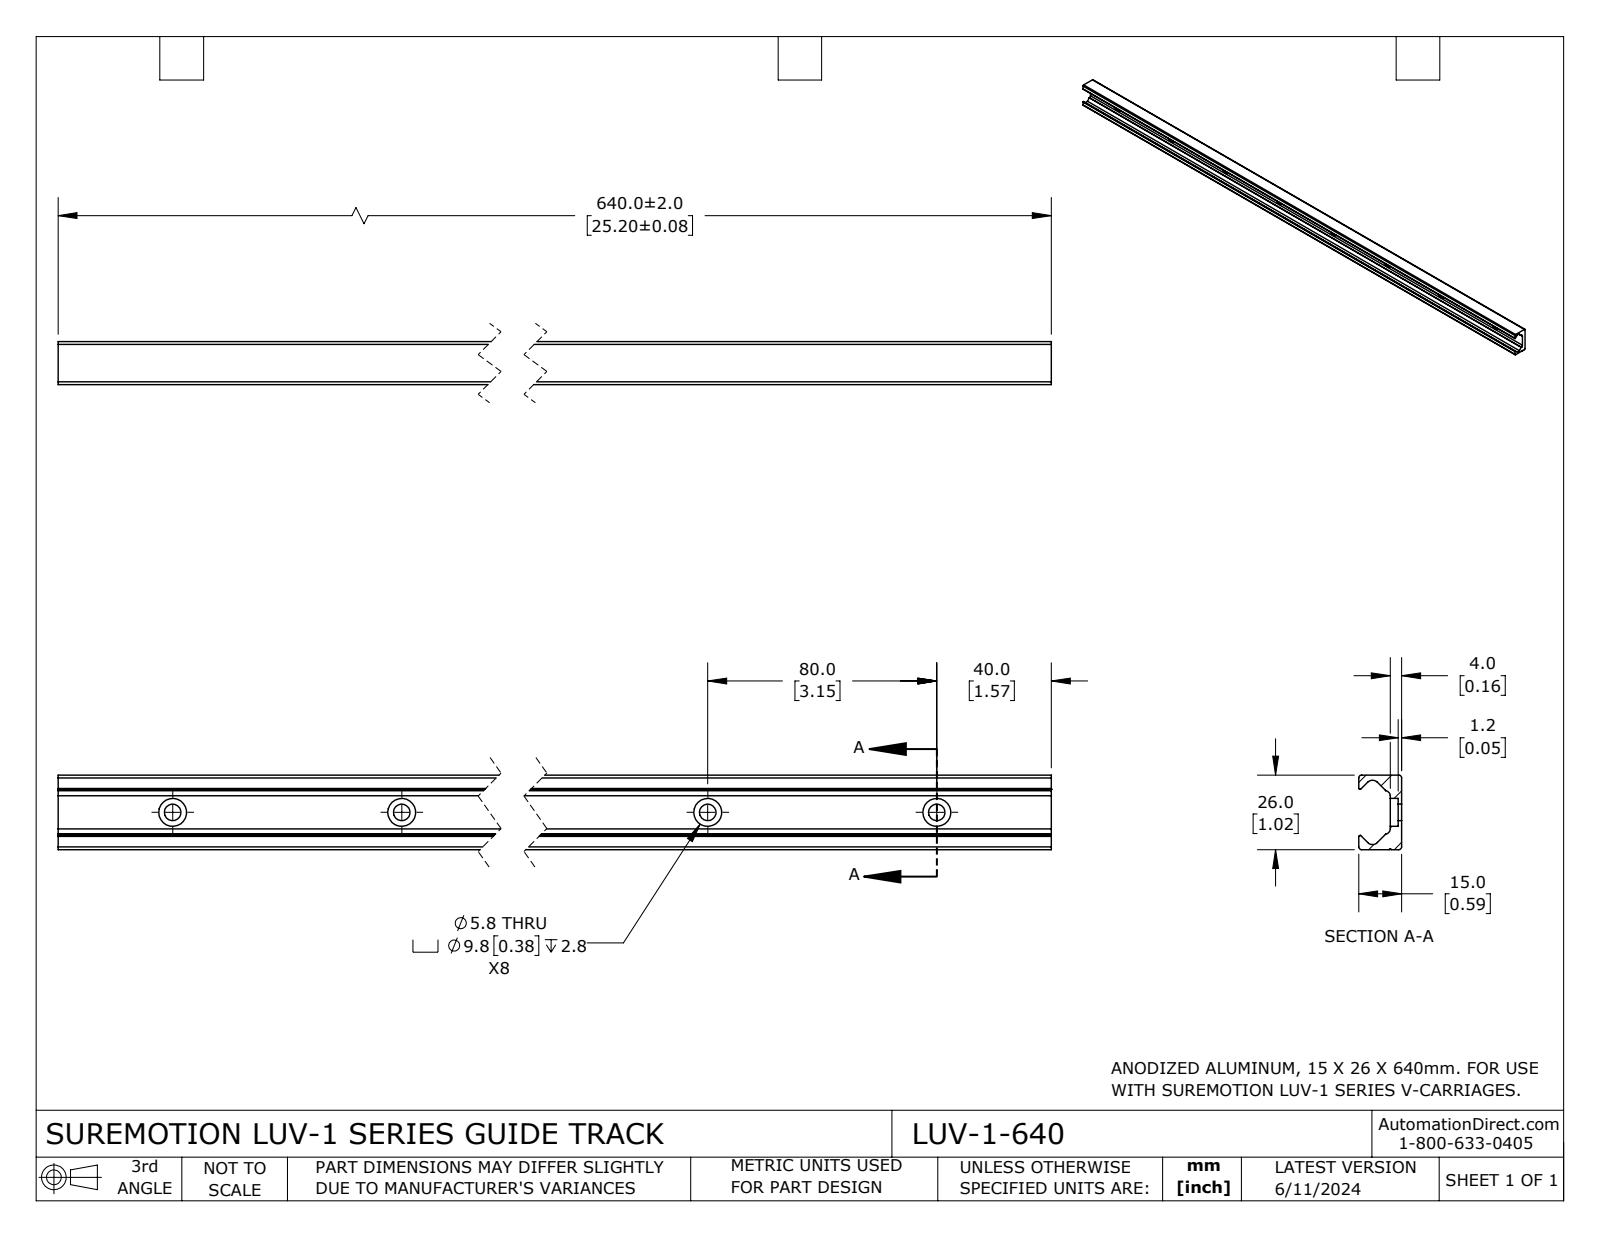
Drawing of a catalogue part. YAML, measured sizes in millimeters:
part_name: "LUV-1-640"
step_written_by: "SolidWorks 2023 (CONFIG_CONTROL_DESIGN)"
units: millimeters
bodies: {solids: 1, faces: 68, planar: 21, cylindrical: 47, other: 0}
overall_size: [640, 26.01, 15.01]
volume: 115238
surface_area: 68068
round_holes:
  - {diameter: 5.79, count: 8}
  - {diameter: 9.75, count: 8}
partial_cylinders:
  - {radius: 0.99, count: 4}
  - {radius: 0.51, count: 2}
  - {radius: 0.64, count: 2}
  - {radius: 0.76, count: 2}
  - {radius: 1.78, count: 2}
  - {radius: 2.39, count: 2}
  - {radius: 0.33, count: 1}
face_to_face_distances: [26.02, 4.01, 15.02, 11.01, 17.27, 1.21, 2.8, 13.81, 640]
hole_center_spacings: [80, 160, 240, 320, 400, 480, 560]
